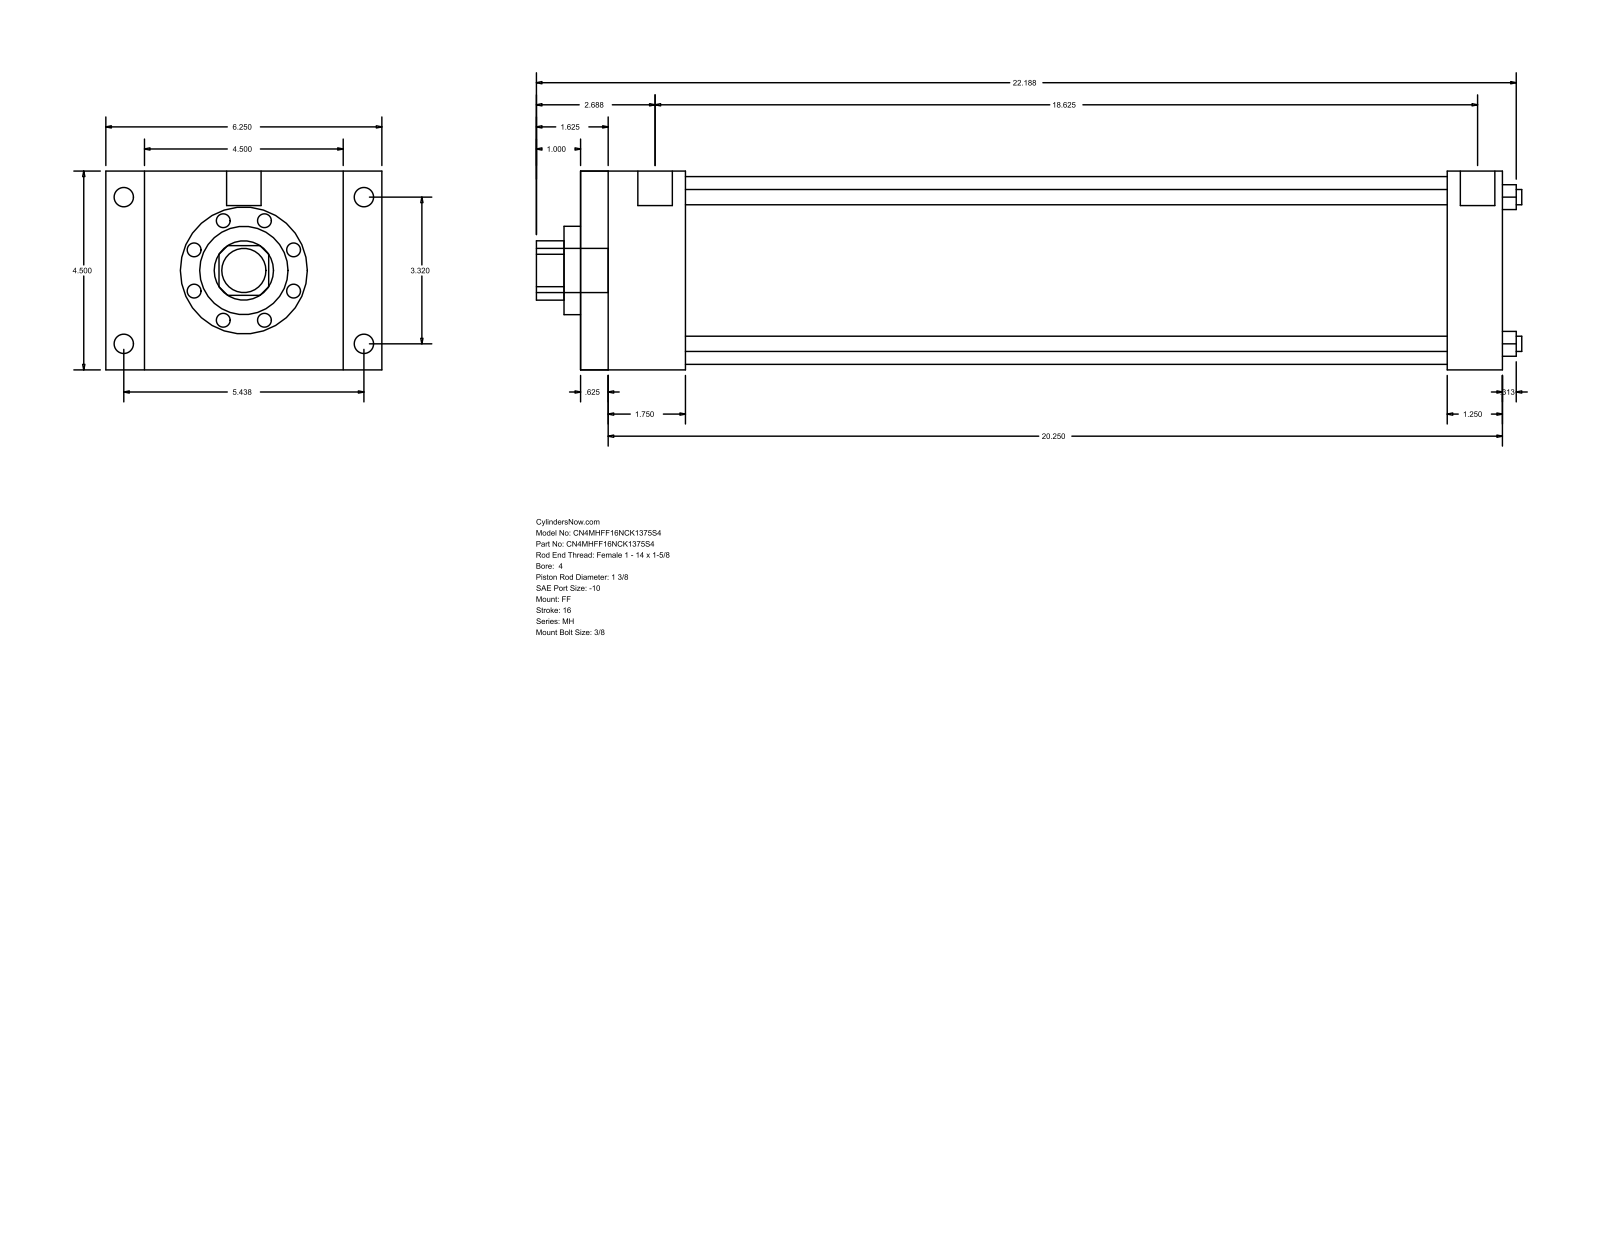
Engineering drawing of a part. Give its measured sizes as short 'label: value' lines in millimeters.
name: MH_FF__0400_1.375
written by: GSSL Pune (CONFIG_CONTROL_DESIGN)
unit: mm
bodies: 0 solids, 92 faces (64 planar, 28 cylindrical, 0 other)
size: 566.74 × 158.75 × 114.3
holes: 4× ⌀8.76, 1× ⌀34.92, 1× ⌀50.8, 1× ⌀107.95
bosses: 4× ⌀11.13, 4× ⌀8.73, 2× ⌀19.84, 1× ⌀25.4
rounds: 1× R17.06
face distances: 114.3, 530.22, 15.87, 514.35, 60.32, 44.45, 469.9, 498.48, 482.61, 438.16
hole spacings: 59.62, 84.32, 119.25
